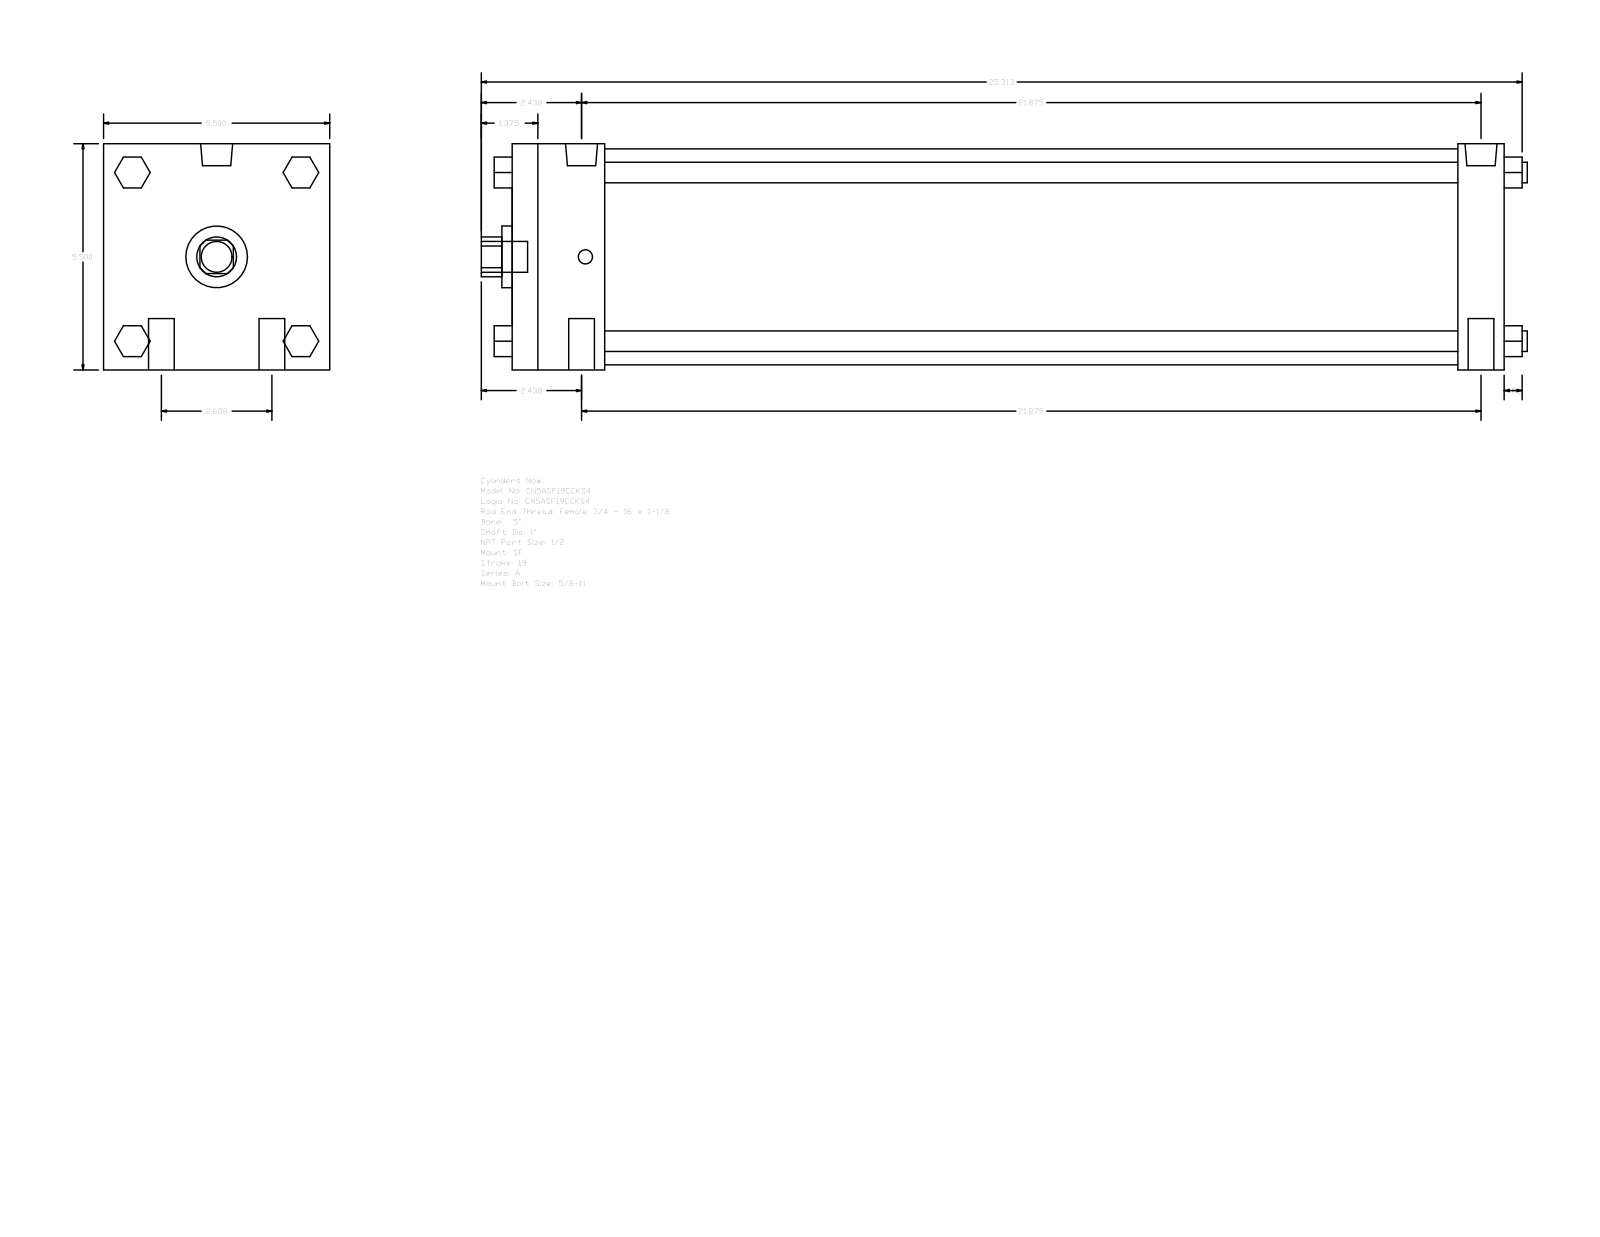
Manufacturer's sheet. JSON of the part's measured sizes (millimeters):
{"part_name": "A_SF__0500_1", "step_written_by": "GSSL Pune (CONFIG_CONTROL_DESIGN)", "units": "millimeters", "bodies": {"solids": 0, "faces": 124, "planar": 94, "cylindrical": 30, "other": 0}, "overall_size": [646.11, 139.7, 139.7], "round_holes": [[25.4, 1], [38.1, 1], [133.35, 1]], "round_bosses_or_shafts": [[15.88, 4], [12.7, 4], [19.77, 2], [8.73, 2], [19.05, 1]], "partial_cylinders_radius": [[12.29, 1]], "face_to_face_distances": [139.7, 612.78, 57.15, 584.2, 527.05, 555.63, 28.58, 19.05, 52.07, 90.18]}
